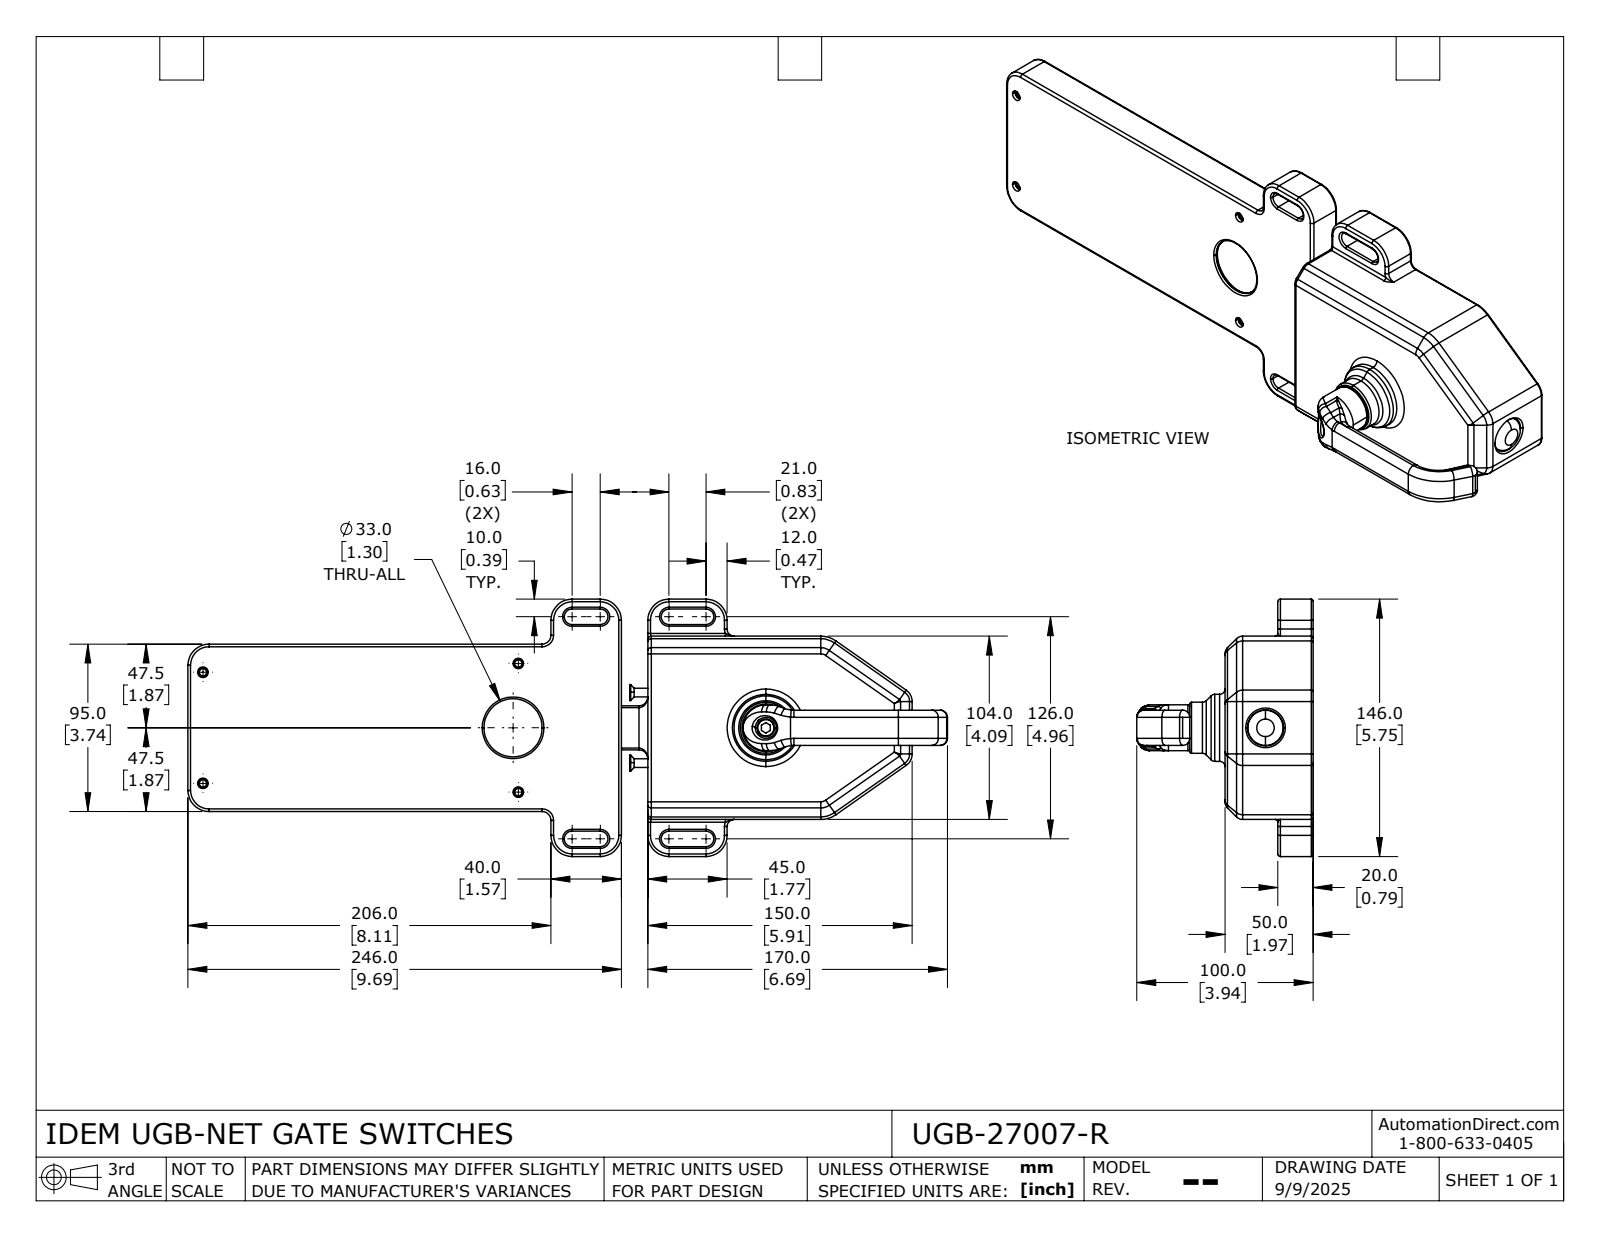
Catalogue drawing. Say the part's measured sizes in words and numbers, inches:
The part is named "527007-R". Its 3-D file was written by "SolidWorks 2024 (AUTOMOTIVE_DESIGN)". It is 15 solids with 2006 faces: 388 planar, 812 cylindrical and 806 other. Overall it measures 16.969 by 5.748 by 3.937 inches. Its volume is 27.96 cubic inches and its surface area 365.7 square inches. Round holes: 10 of diameter 0.165, 4 of diameter 0.217, 4 of diameter 0.236, 2 of diameter 0.13, 2 of diameter 0.413, 1 of diameter 0.157, 1 of diameter 0.177, 1 of diameter 0.248, 1 of diameter 0.268, 1 of diameter 0.294, 1 of diameter 0.472, 1 of diameter 0.559. Round bosses or shafts: 5 of diameter 0.236, 4 of diameter 0.433, 2 of diameter 0.787, 2 of diameter 0.394, 2 of diameter 0.354, 2 of diameter 0.276, 2 of diameter 0.197, 1 of diameter 1.496. Partial cylindrical surfaces (rounded edges, fillets, slot ends): 277 of radius 0.039, 88 of radius 0.079, 26 of radius 0.118, 26 of radius 0.197, 21 of radius 0.059, 19 of radius 0.031, 16 of radius 0.02, 12 of radius 0.018. The main face-to-face distances are 0.098, 0.65, 0.138, 0.748, 0.039, 1.831, 1.28, 1.693, 1.181, 1.929. The hole center spacings are 6.538, 13.482, 1.571, 3.284, 0.812, 0.846, 1.442, 1.535.
